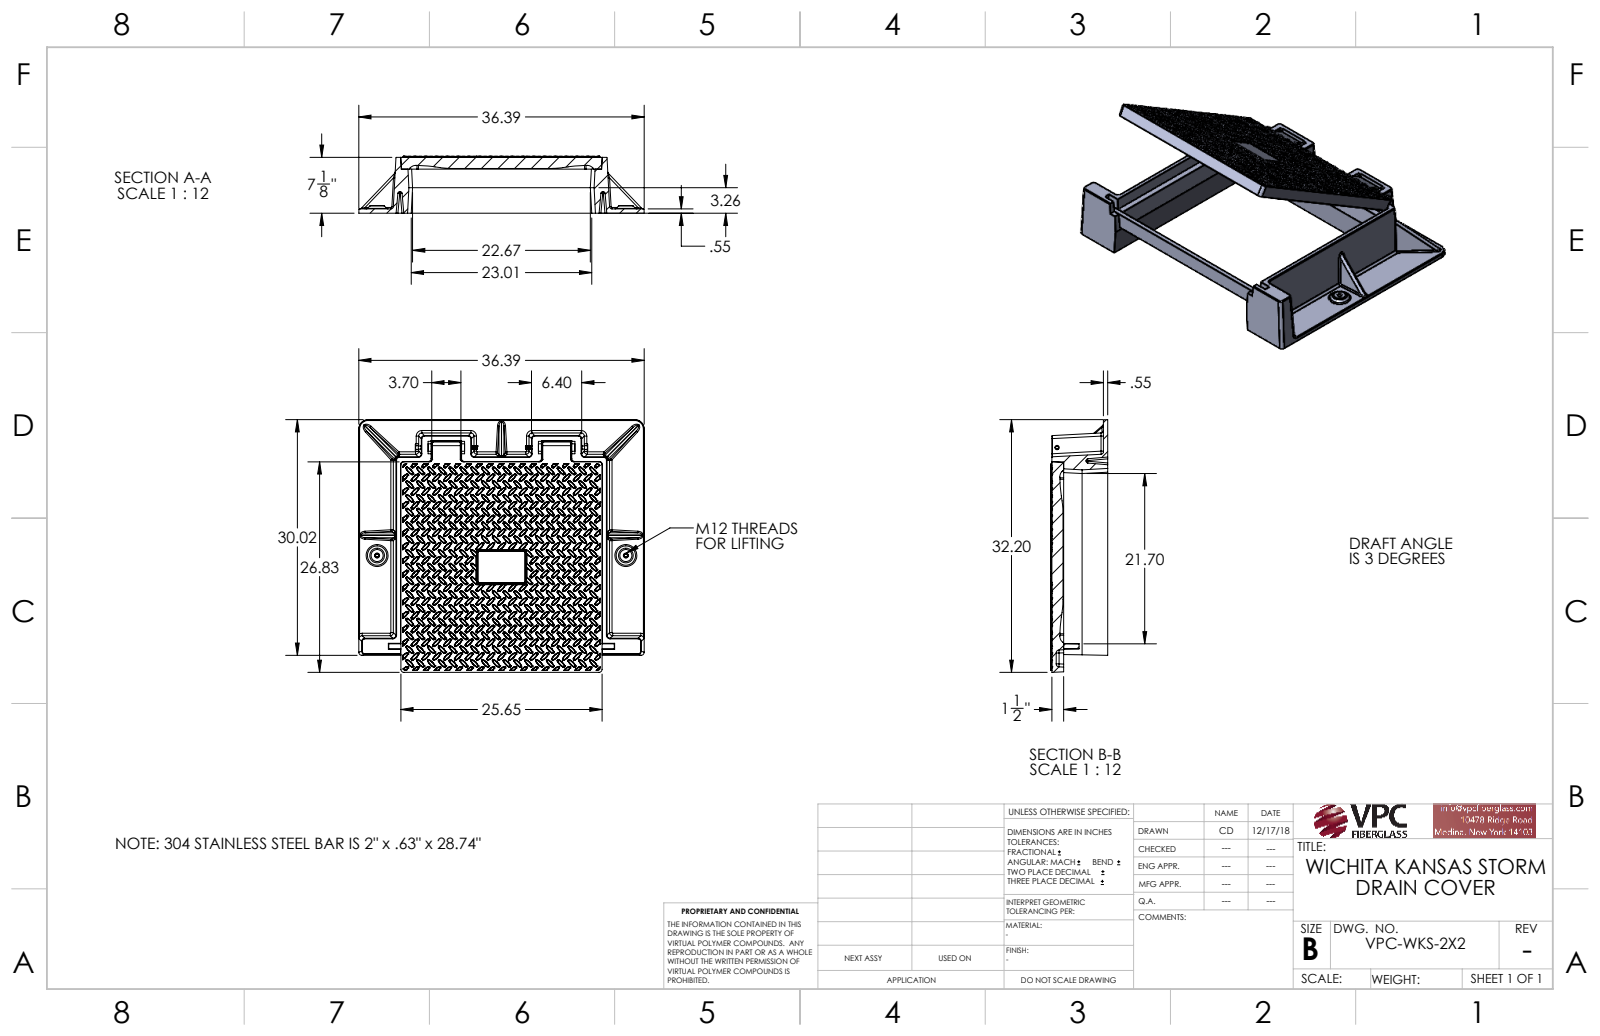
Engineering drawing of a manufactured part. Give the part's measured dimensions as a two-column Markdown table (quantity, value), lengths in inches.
| quantity | value |
| --- | --- |
| part name | B180 681.482x651.51 ZOU; B180 681.482x651.51 GAI; VPC-WKS-2X2 |
| STEP written by | SolidWorks 2020 (AUTOMOTIVE_DESIGN) |
| units | inches |
| bodies | 564 solids, 15780 faces (890 planar, 524 cylindrical, 14366 other) |
| overall size | 36.39 × 32.2 × 7.275 |
| volume | 2 209 in³ |
| surface area | 5 277 in² |
| round holes (diameter × count) | 0.551 × 3, 0.394 × 2, 0.472 × 2 |
| round bosses / shafts (diameter × count) | 0.63 × 2, 0.394 × 1, 0.336 × 1 |
| partial cylindrical surfaces (radius × count) | 0.236 × 70, 0.394 × 38, 0.197 × 28, 0.079 × 27, 0.315 × 25, 0.039 × 8, 0.059 × 8, 19.685 × 8 |
| main face-to-face distances | 7.125, 0.551, 6.574, 7.137, 6.585, 5.625, 5.074, 1.5, 1.512, 1.849 |
| hole center spacings | 31.716 |
